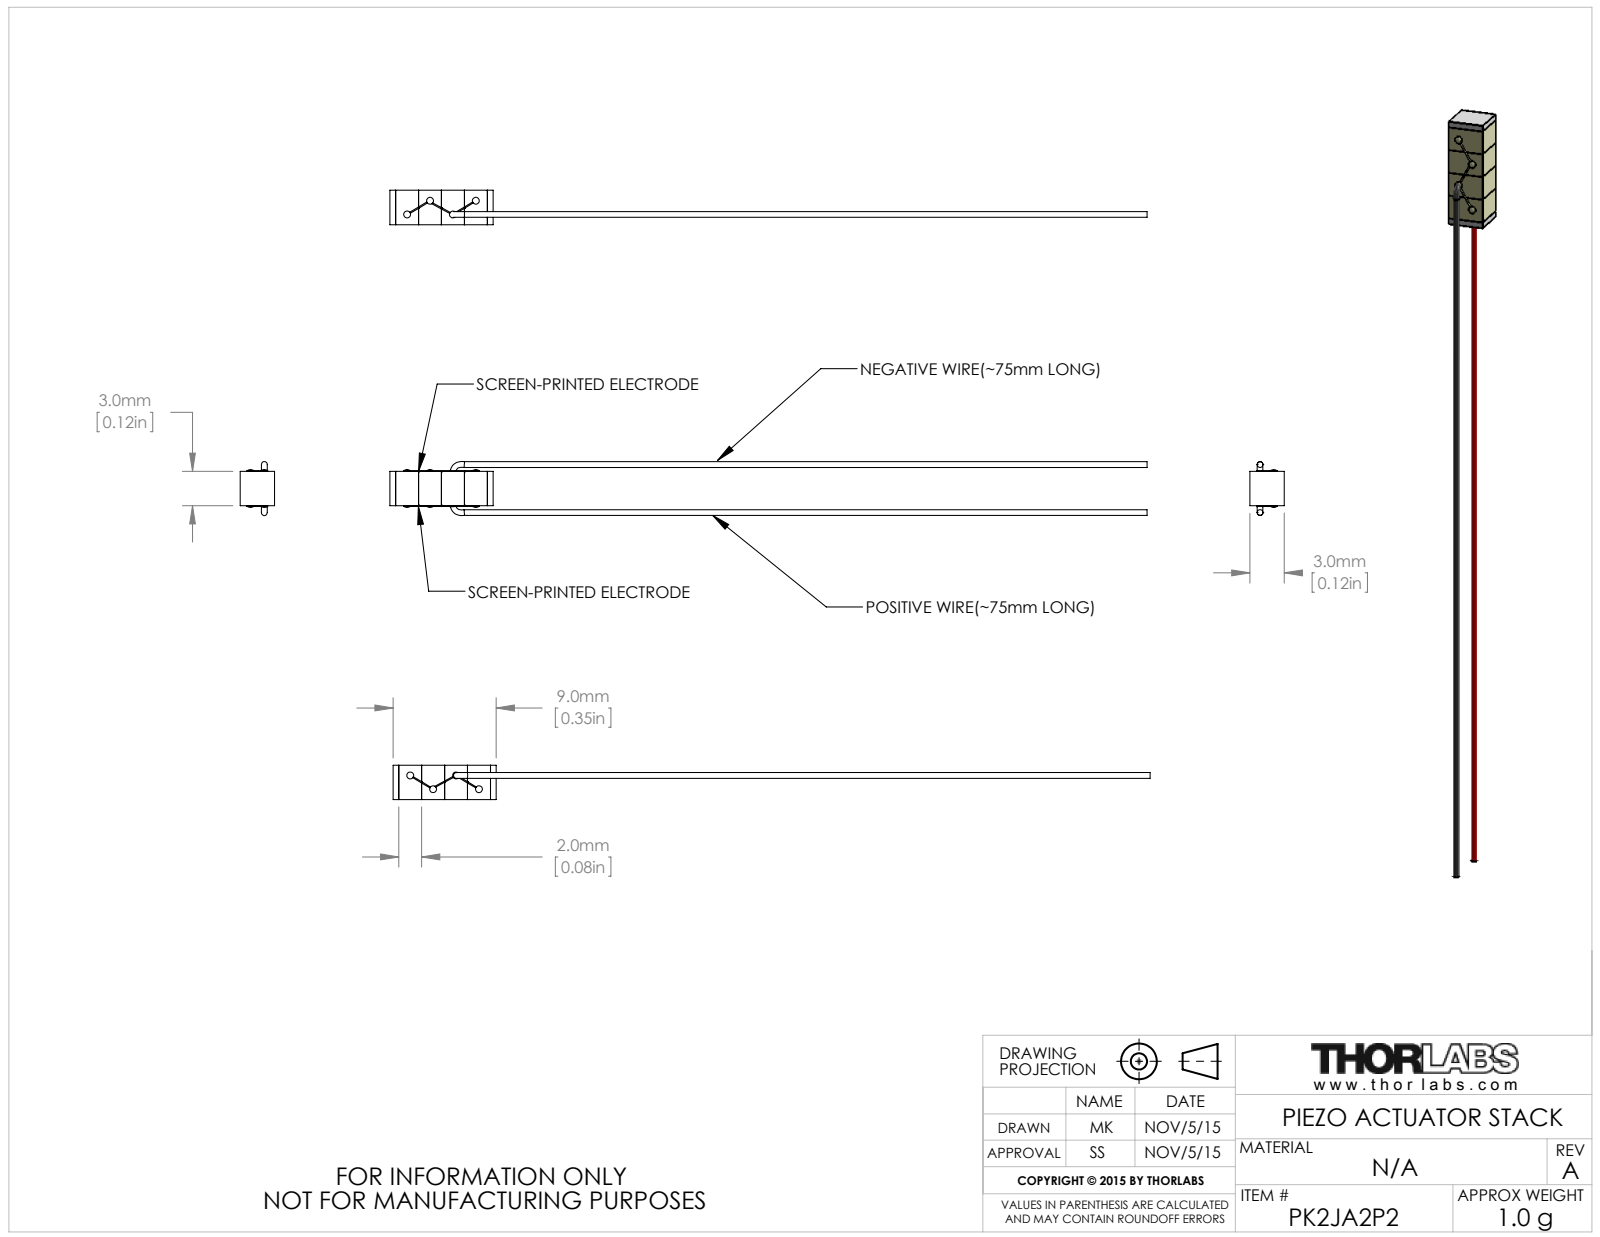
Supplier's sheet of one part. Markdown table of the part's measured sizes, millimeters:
| quantity | value |
| --- | --- |
| part name | CTN003248 |
| STEP written by | SolidWorks 2014 (AUTOMOTIVE_DESIGN) |
| units | millimeters |
| bodies | 4 solids, 103 faces (43 planar, 36 cylindrical, 24 other) |
| overall size | 66.1 × 4.72 × 3 |
| volume | 105 mm³ |
| surface area | 410 mm² |
| round bosses / shafts (diameter × count) | 0.6 × 4 |
| main face-to-face distances | 2, 3, 4, 6, 0.5, 8.51, 2.51, 4.51, 6.51, 2.01 |
